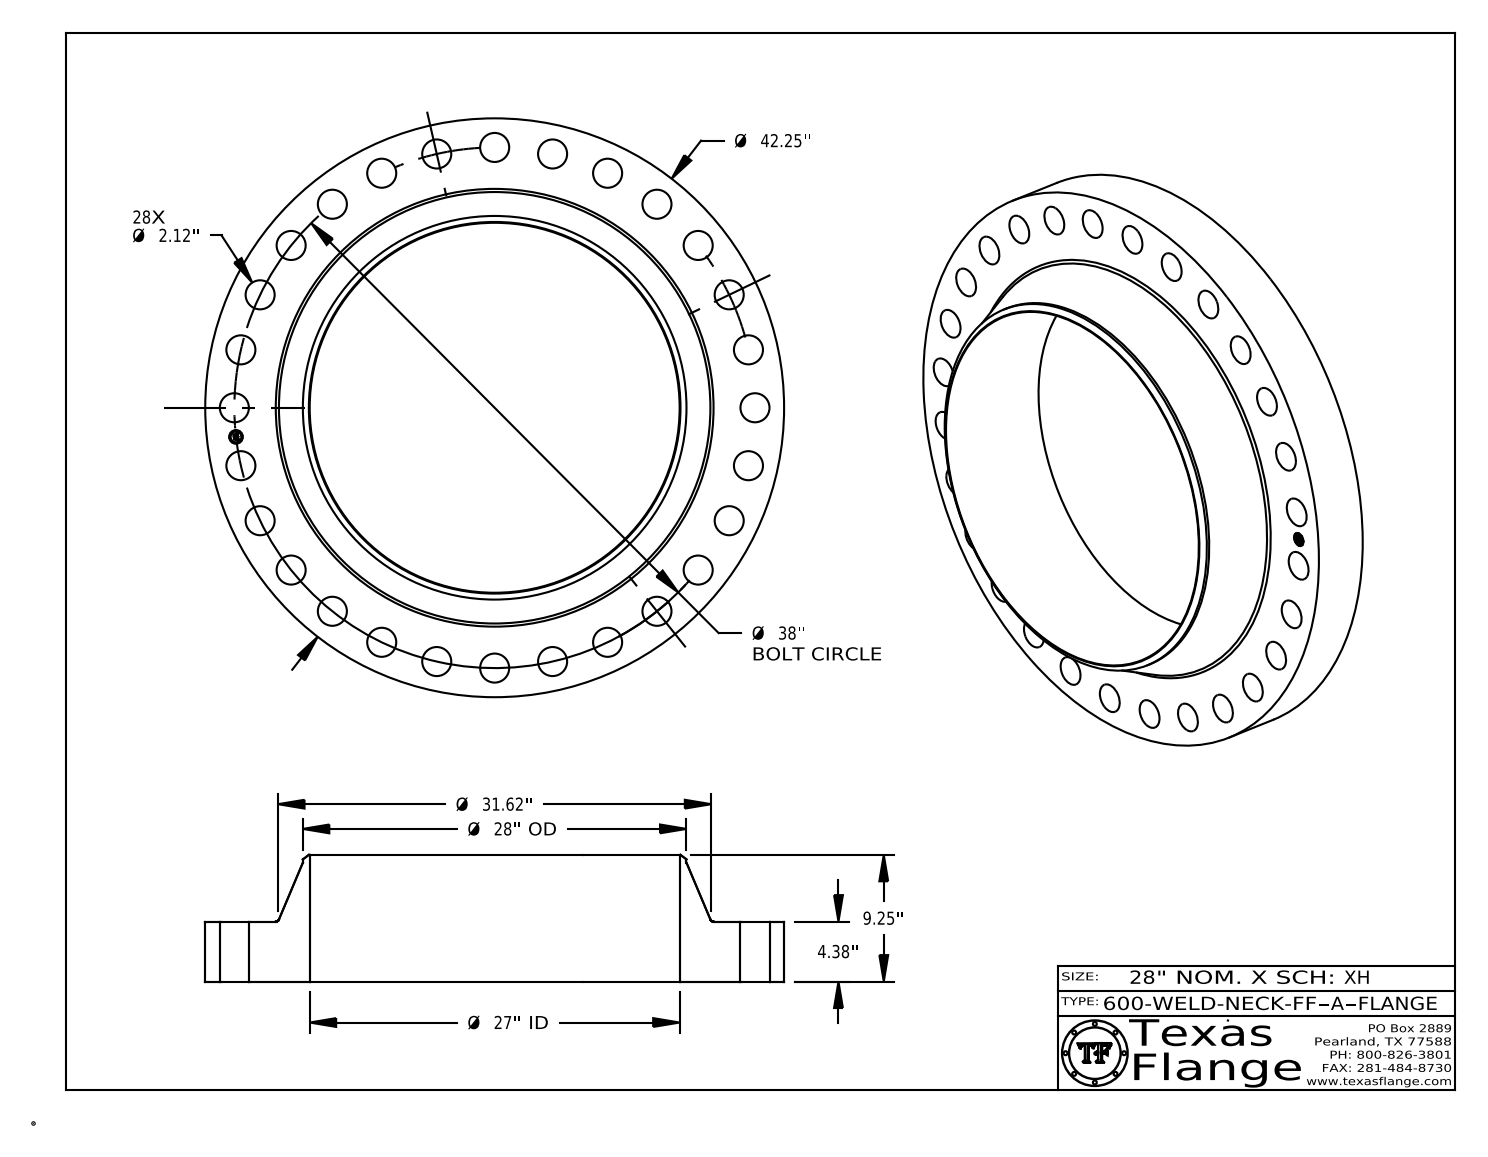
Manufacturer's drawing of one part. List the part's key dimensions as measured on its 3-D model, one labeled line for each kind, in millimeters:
Part name (STEP PRODUCT): 600-WELD-NECK-FF, Series A
STEP written by: CATIA V5 STEP AP214 (AUTOMOTIVE_DESIGN)
Units: millimetres
Bodies: 1 solid, 456 faces (368 planar, 82 cylindrical, 6 other)
Overall size (bounding box): 1073.2 × 1073.2 × 235
Volume: 61 630 000 mm³ · Surface area: 2 541 000 mm²
Round holes (diameter × count): ⌀53.8 ×28, ⌀25.4 ×1, ⌀685.8 ×1
Round bosses / shafts (diameter × count): ⌀1.5 ×8, ⌀1073.2 ×1, ⌀711.2 ×1, ⌀20 ×1
Main face-to-face distances: 111.3, 235, 123.7, 110.9, 0.4, 124.1, 7.6, 7.4, 1.4, 4.9
Hole centre spacings: 482.6, 513.5, 682.5, 817.3, 911, 941, 959.1, 214.8
